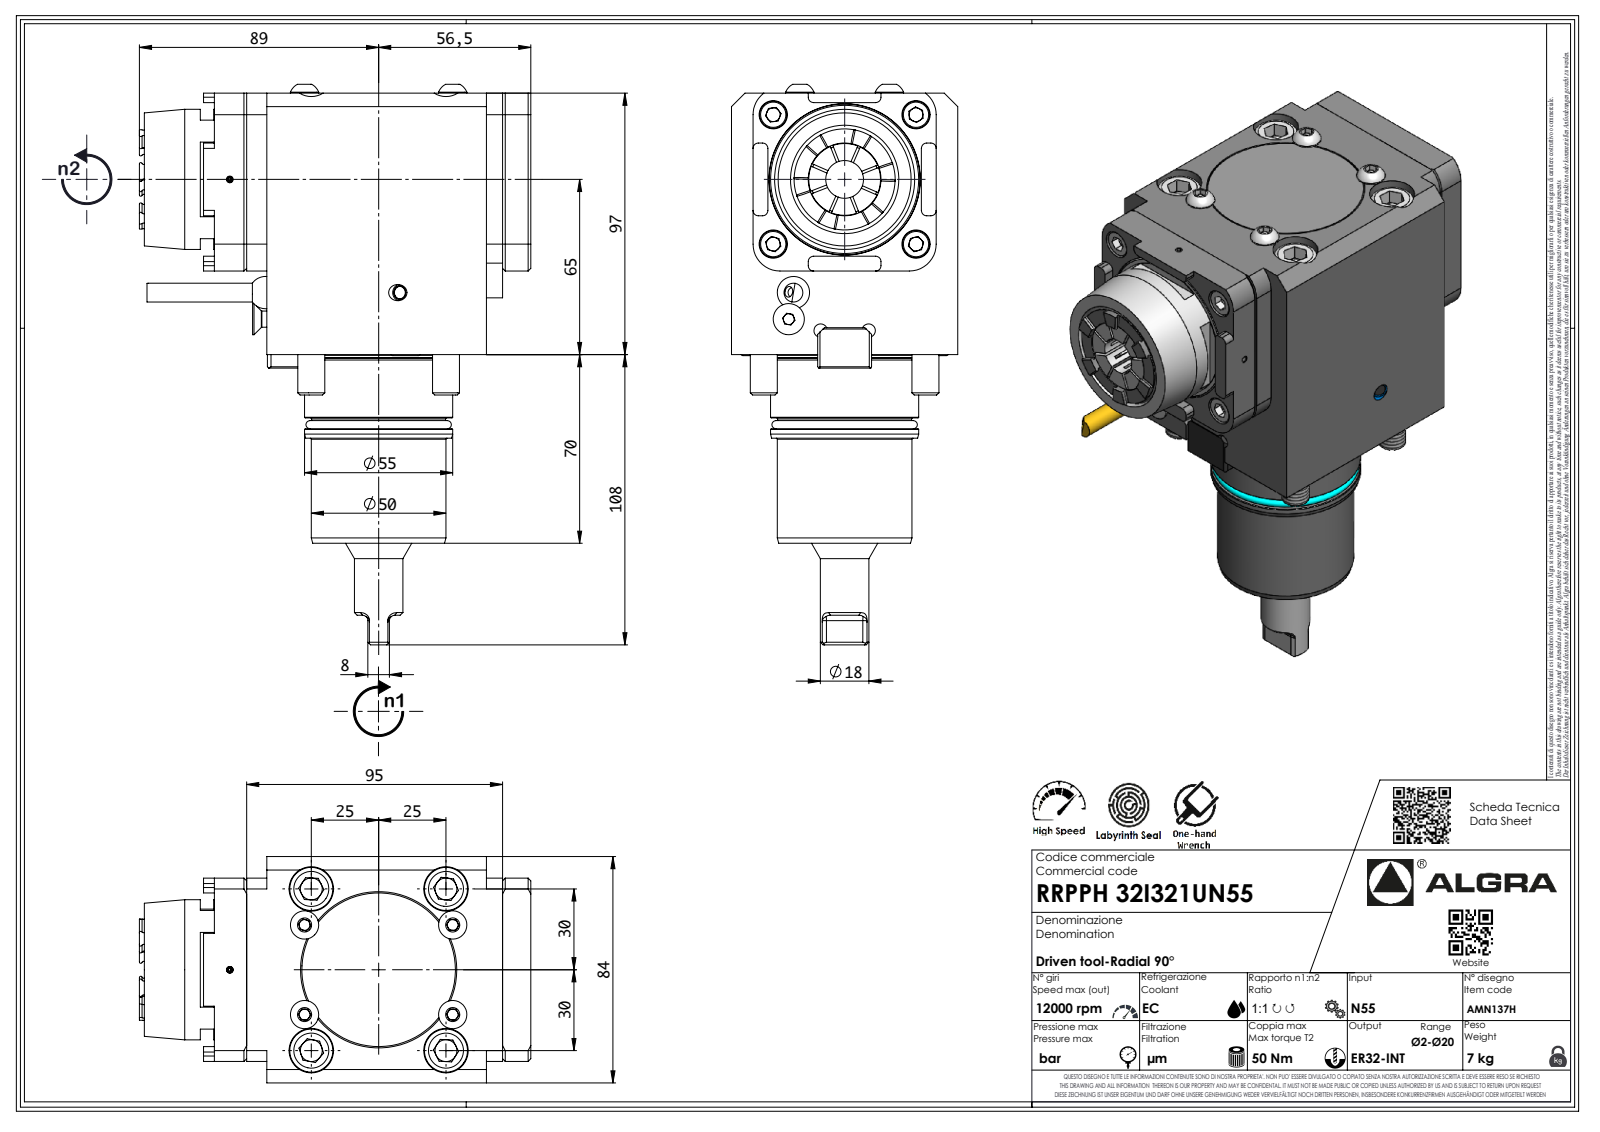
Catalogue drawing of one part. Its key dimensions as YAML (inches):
part_name: "RRPPH32I321UN55"
step_written_by: "SolidWorks 2023 (AUTOMOTIVE_DESIGN)"
units: inches
bodies: {solids: 1, faces: 579, planar: 329, cylindrical: 98, other: 152}
overall_size: [8.059, 5.721, 3.307]
volume: 63.22
surface_area: 118.6
round_holes:
  - {diameter: 0.124, count: 1}
  - {diameter: 0.337, count: 1}
  - {diameter: 0.472, count: 1}
  - {diameter: 2.283, count: 1}
round_bosses_or_shafts:
  - {diameter: 2.165, count: 1}
  - {diameter: 2.15, count: 1}
  - {diameter: 2.047, count: 1}
  - {diameter: 1.969, count: 1}
  - {diameter: 1.957, count: 1}
  - {diameter: 0.709, count: 1}
  - {diameter: 0.456, count: 1}
  - {diameter: 0.376, count: 1}
partial_cylinders:
  - {radius: 0.079, count: 20}
  - {radius: 0.02, count: 7}
  - {radius: 0.031, count: 7}
  - {radius: 0.219, count: 7}
  - {radius: 0.394, count: 4}
  - {radius: 0.098, count: 3}
  - {radius: 0.012, count: 1}
  - {radius: 0.118, count: 1}
face_to_face_distances: [3.307, 3.819, 0.315, 2.992, 3.858, 0.65, 3.209, 3.976, 3.817, 1.024]
